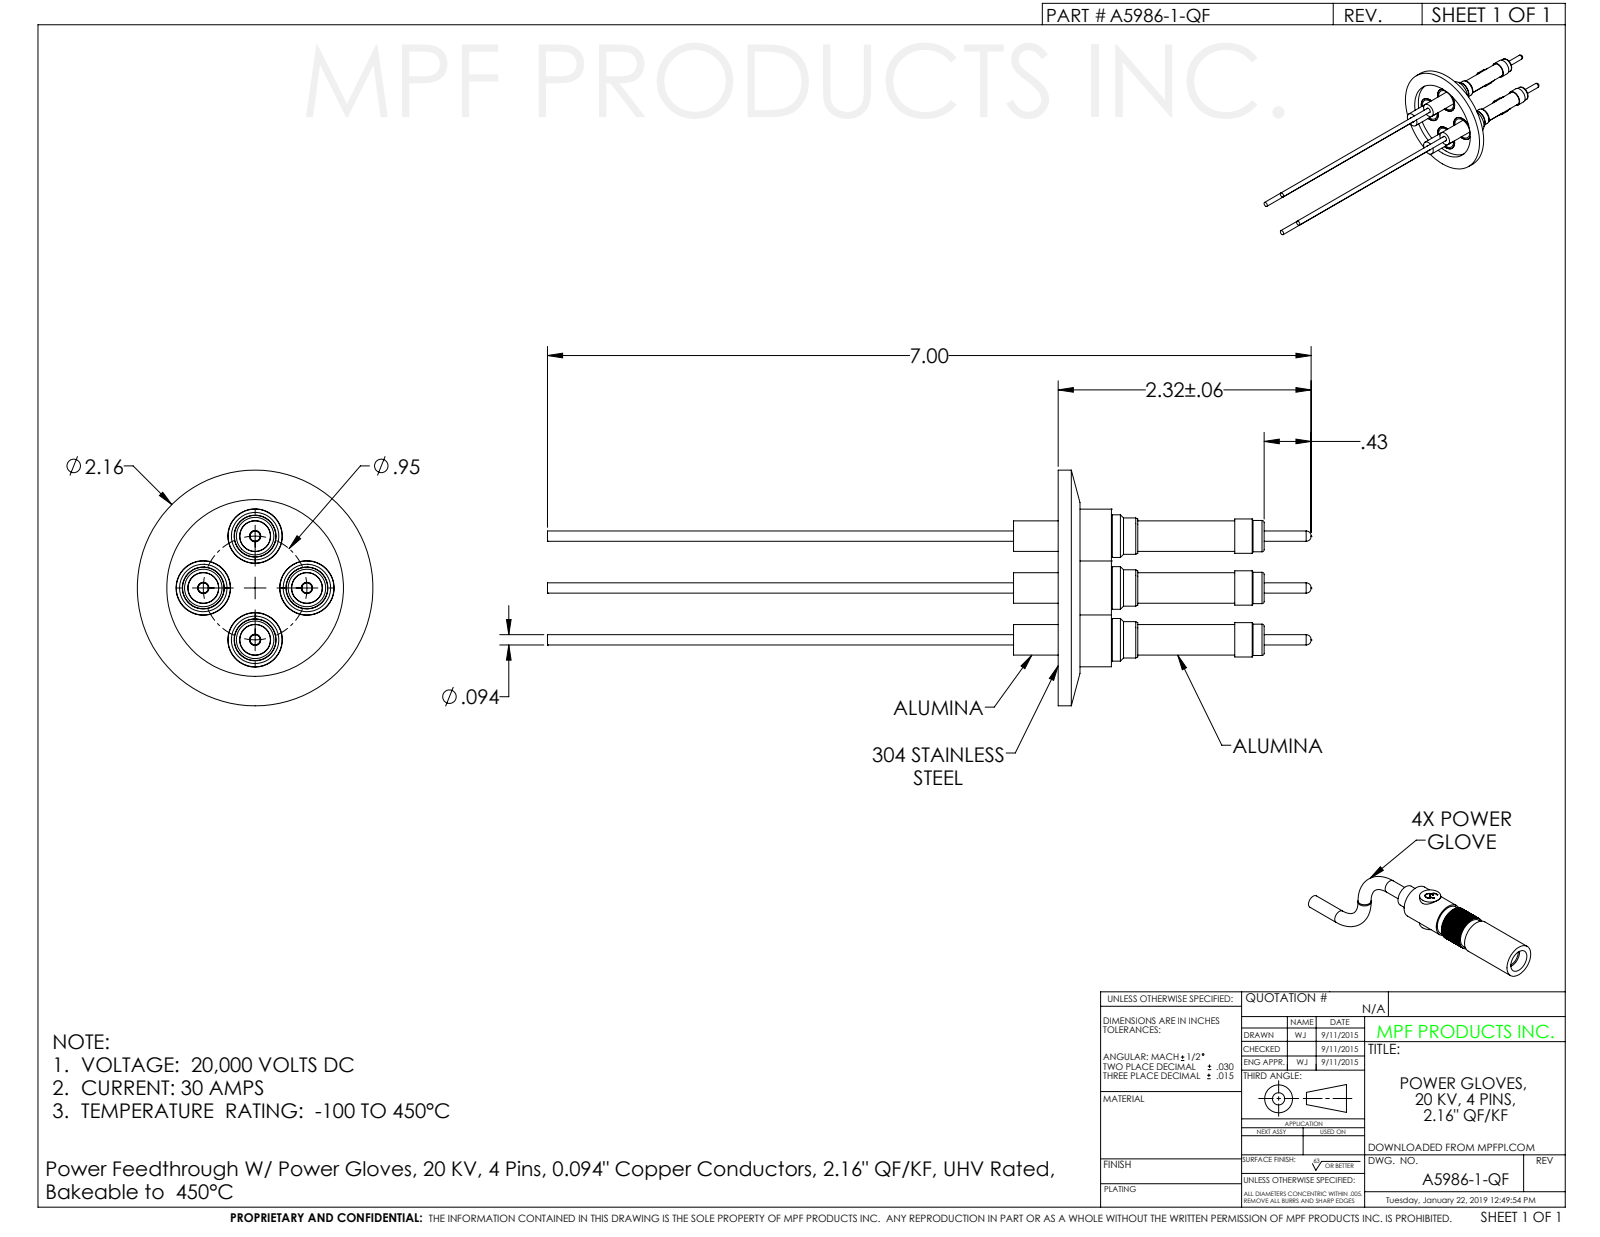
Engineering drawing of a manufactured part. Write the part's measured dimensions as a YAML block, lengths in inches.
part_name: "A5986-1-QF"
step_written_by: "SolidWorks 2012 (CONFIG_CONTROL_DESIGN)"
units: inches
bodies: {solids: 1, faces: 261, planar: 47, cylindrical: 124, other: 90}
overall_size: [7, 2.161, 2.161]
volume: 1.15
surface_area: 33.97
round_holes:
  - {diameter: 0.259, count: 4}
  - {diameter: 0.344, count: 4}
  - {diameter: 0.385, count: 4}
  - {diameter: 0.435, count: 4}
  - {diameter: 0.105, count: 2}
  - {diameter: 0.105, count: 2}
  - {diameter: 1.63, count: 1}
round_bosses_or_shafts:
  - {diameter: 0.495, count: 4}
  - {diameter: 0.391, count: 4}
  - {diameter: 0.372, count: 4}
  - {diameter: 0.312, count: 4}
  - {diameter: 0.306, count: 4}
  - {diameter: 0.287, count: 4}
  - {diameter: 0.28, count: 4}
  - {diameter: 0.094, count: 4}
face_to_face_distances: [0.105, 0.2, 0.095, 0.488, 0.383, 0.288, 0.4, 0.505, 0.6, 0.888]
hole_center_spacings: [0.475, 0.672, 0.95]
